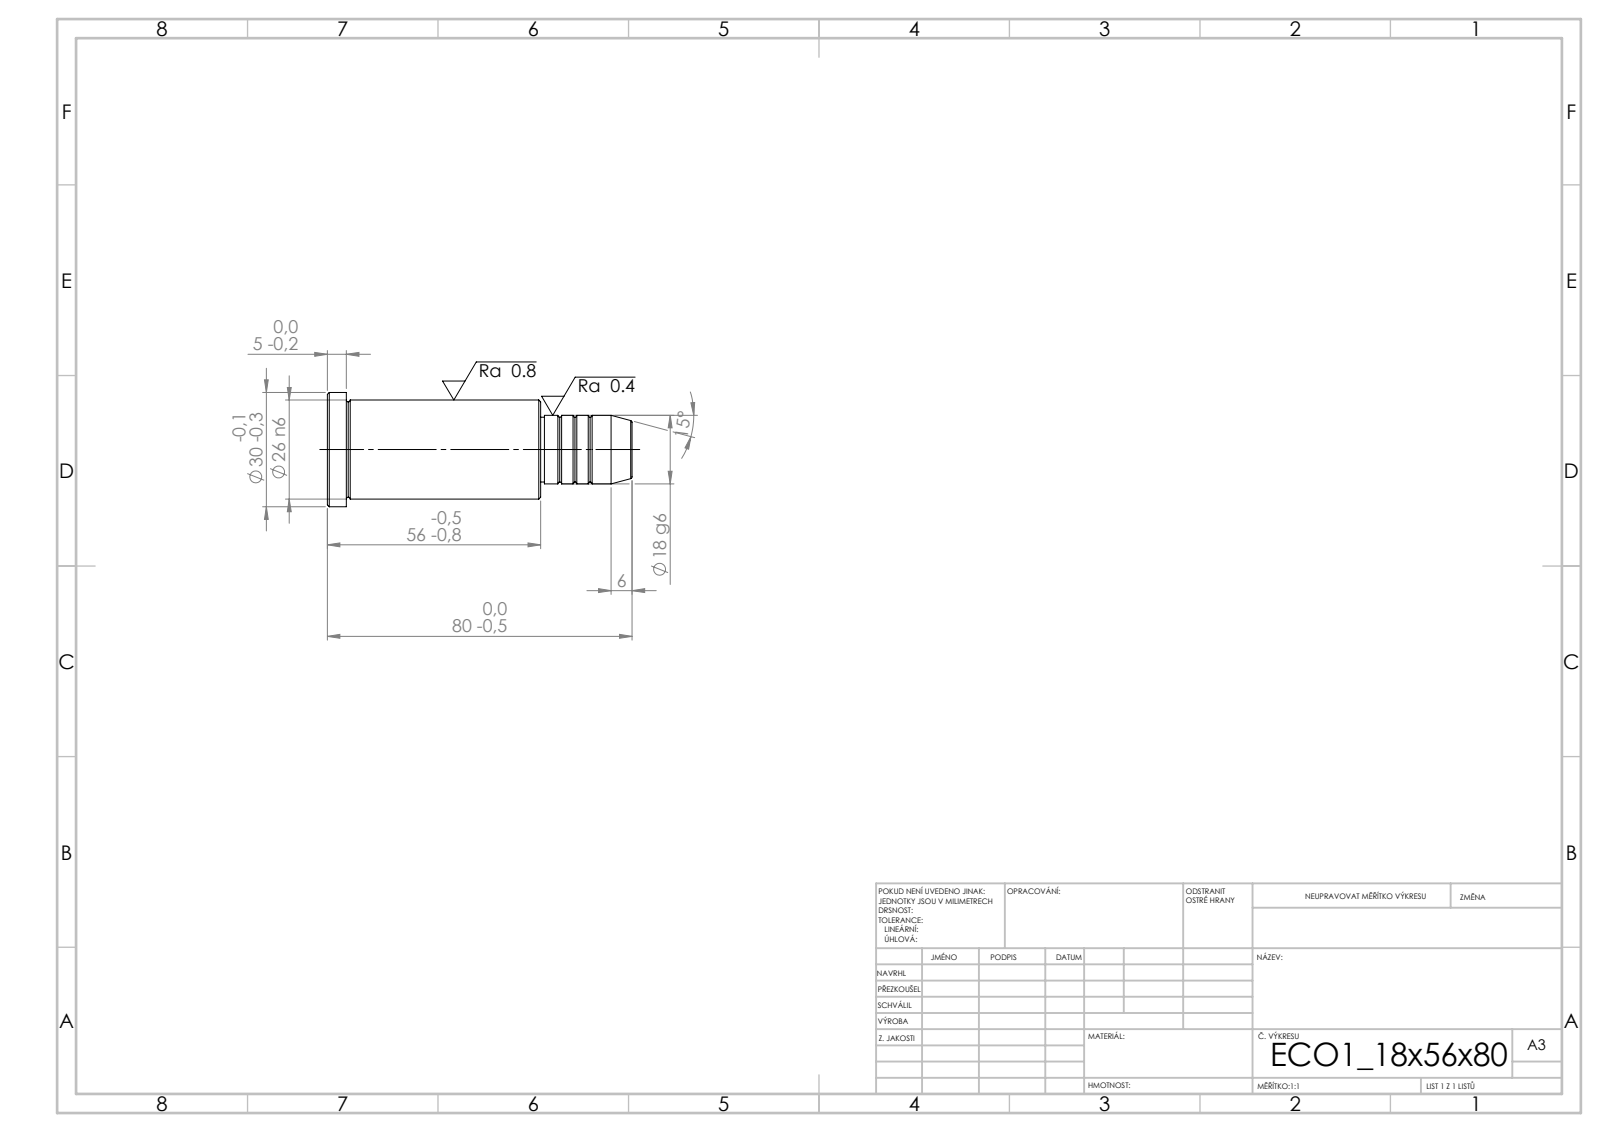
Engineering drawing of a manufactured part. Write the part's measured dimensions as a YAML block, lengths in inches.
step_written_by: "SolidWorks 2019 (CONFIG_CONTROL_DESIGN)"
units: inches
bodies: {solids: 1, faces: 43, planar: 5, cylindrical: 14, other: 24}
overall_size: [3.15, 1.181, 1.181]
volume: 2.219
surface_area: 11.53
round_bosses_or_shafts:
  - {diameter: 1.181, count: 1}
  - {diameter: 1.024, count: 1}
  - {diameter: 0.709, count: 1}
  - {diameter: 0.669, count: 1}
face_to_face_distances: [2.205, 2.008, 0.197, 0.945, 2.953, 3.15, 0.906, 0.039, 2.047, 2.244]
